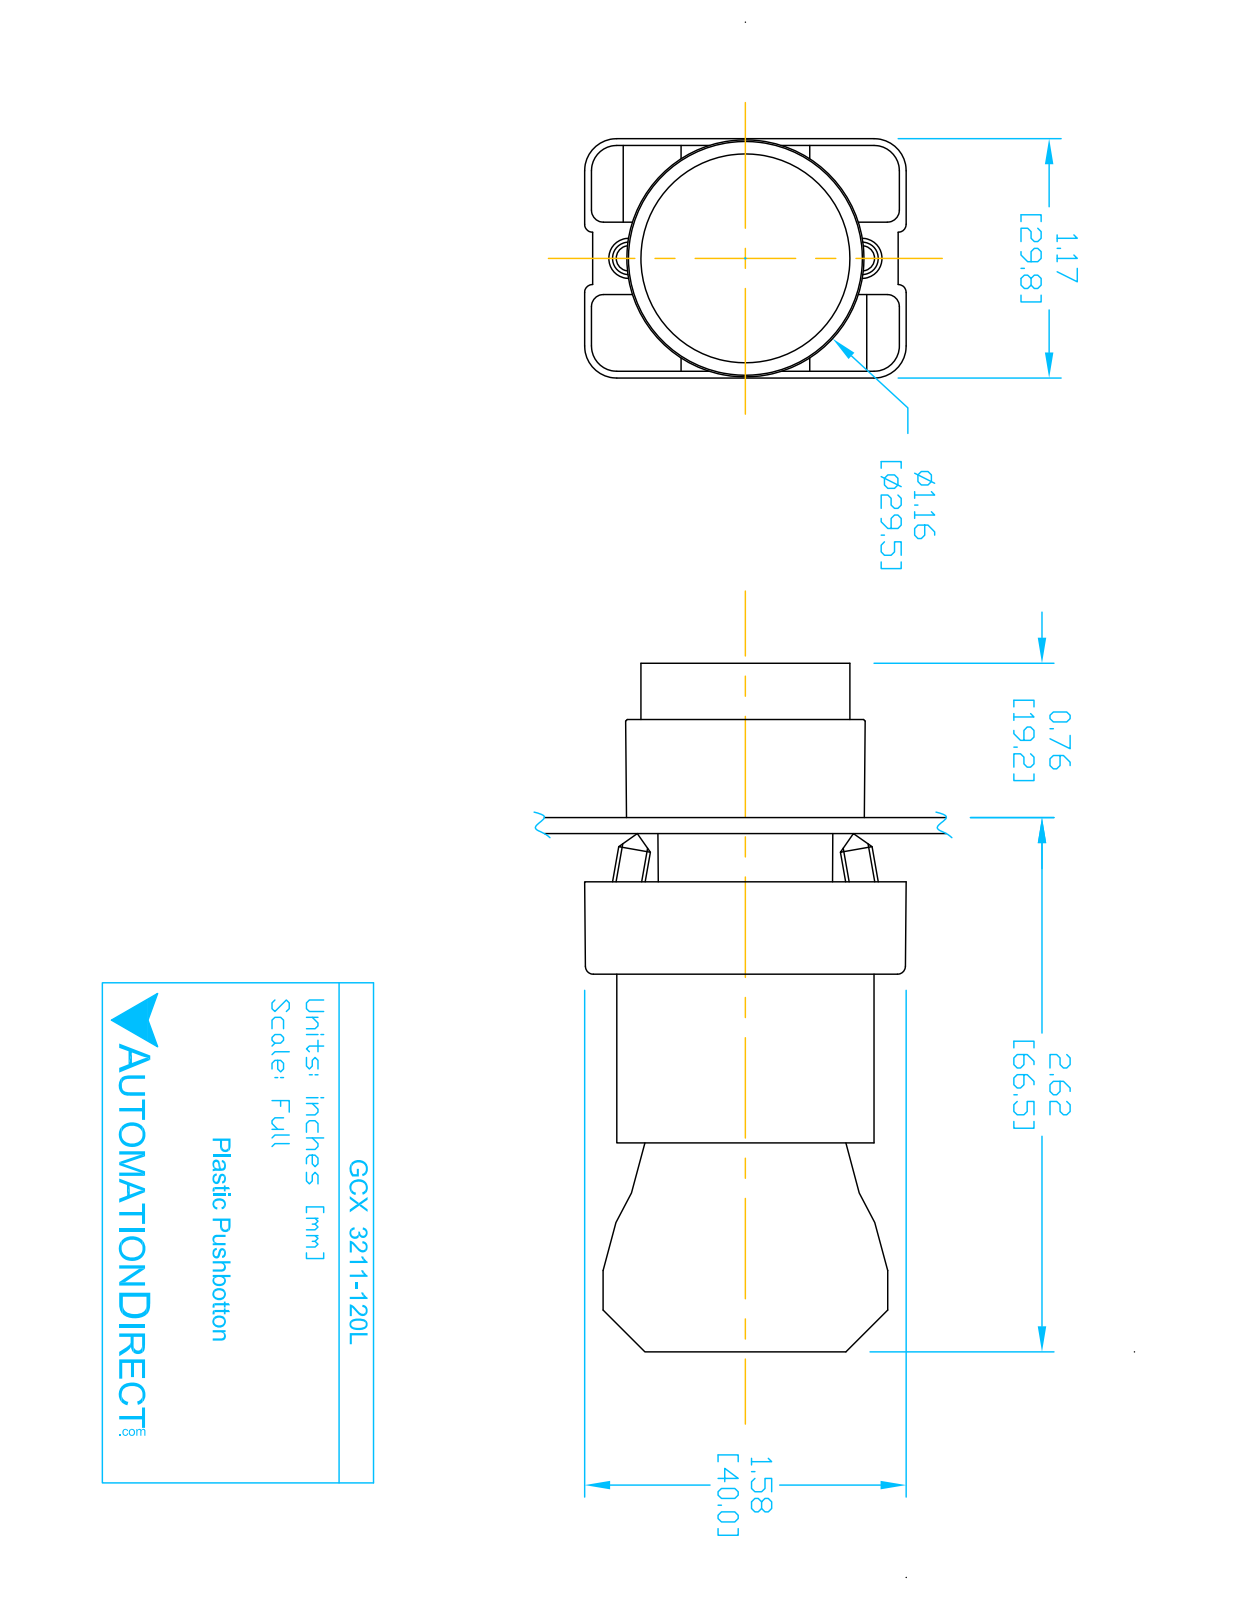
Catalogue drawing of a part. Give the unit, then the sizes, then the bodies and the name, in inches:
Units: inches
Overall size (bounding box): 3.319 × 1.581 × 1.177
Round holes (diameter × count): ⌀0.079 ×2, ⌀0.124 ×2, ⌀0.13 ×2, ⌀0.087 ×1, ⌀0.197 ×1, ⌀0.469 ×1, ⌀0.878 ×1, ⌀0.888 ×1, ⌀1.024 ×1
Round bosses / shafts (diameter × count): ⌀0.157 ×4, ⌀1.175 ×1, ⌀1.004 ×1, ⌀0.945 ×1, ⌀0.856 ×1, ⌀0.78 ×1, ⌀0.504 ×1
Partial cylindrical surfaces — rounded edges, fillets, slot ends (radius × count): R0.059 ×24, R0.041 ×12, R0.124 ×12, R0.157 ×12, R0.039 ×8, R0.128 ×2, R0.02 ×1, R0.063 ×1
Main face-to-face distances: 0.827, 0.579, 1.171, 2.02, 1.193, 0.031, 0.033, 0.573, 1.165, 0.593
Hole centre spacings: 0.236, 0.544, 0.472, 0.49
Volume: 2.721 in³ · Surface area: 36.32 in²
Bodies: 7 solids, 425 faces (250 planar, 144 cylindrical, 31 other)
Part name (STEP PRODUCT): GCX3211-120L; ECX3029-2; ECX1050; ecx1030 (+1 more)
STEP written by: SolidWorks 2016 (AUTOMOTIVE_DESIGN)
